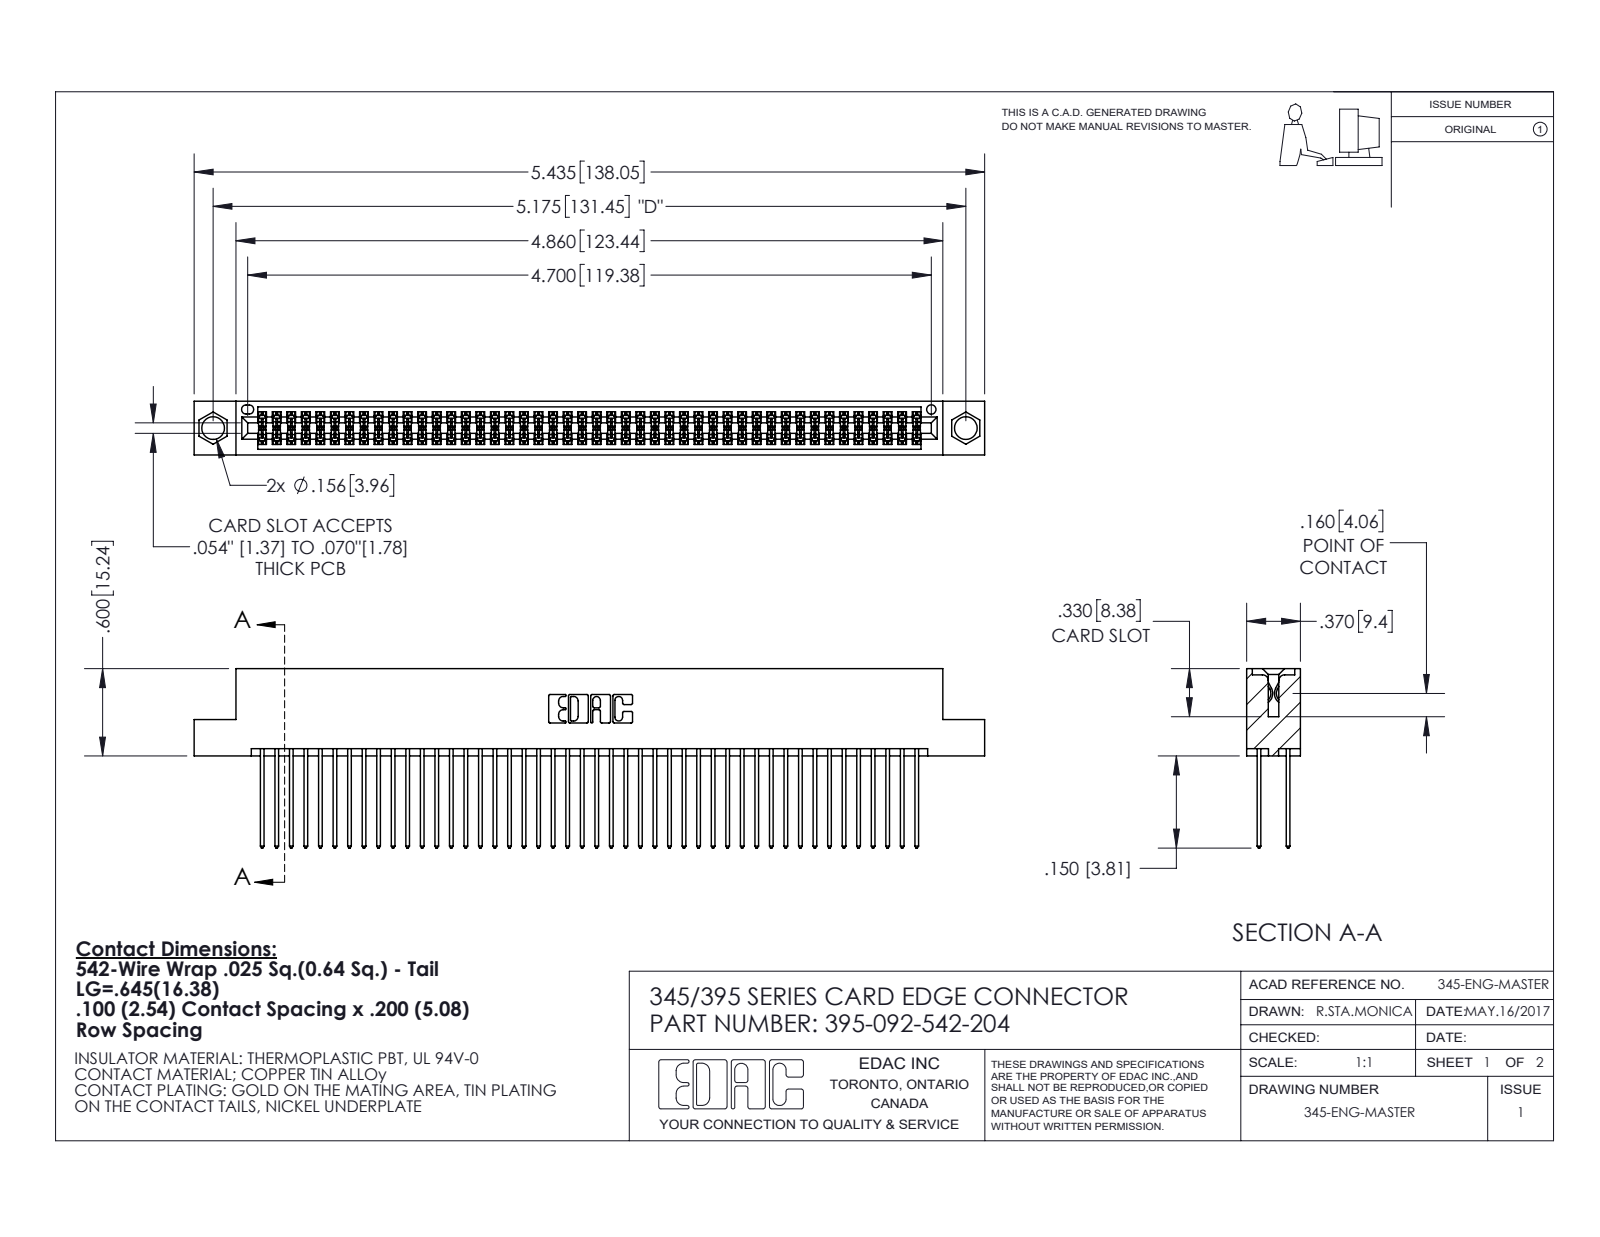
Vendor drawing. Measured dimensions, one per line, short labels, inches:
name: 345-292-001_345-293-142; 395-092-542-204; 345 Part_Flush Mounting Lugs - 0.156 Dia-TI
written by: SolidWorks 2020 (CONFIG_CONTROL_DESIGN)
unit: in
bodies: 93 solids, 4740 faces (3130 planar, 1610 cylindrical, 0 other)
size: 5.435 × 1.232 × 0.37
volume: 0.84 in³; area: 34.55 in²
holes: 2× ⌀0.156, 1× ⌀0.064
rounds: 138× R0.006, 92× R0.01, 22× R0.01, 6× R0.007, 6× R0.031, 3× R0.026, 2× R0.014, 2× R0.019
face distances: 0.298, 0.072, 0.2, 0.098, 0.272, 0.025, 0.225, 0.37, 0.175, 0.149
hole spacings: 0.27, 4.939, 5.175
